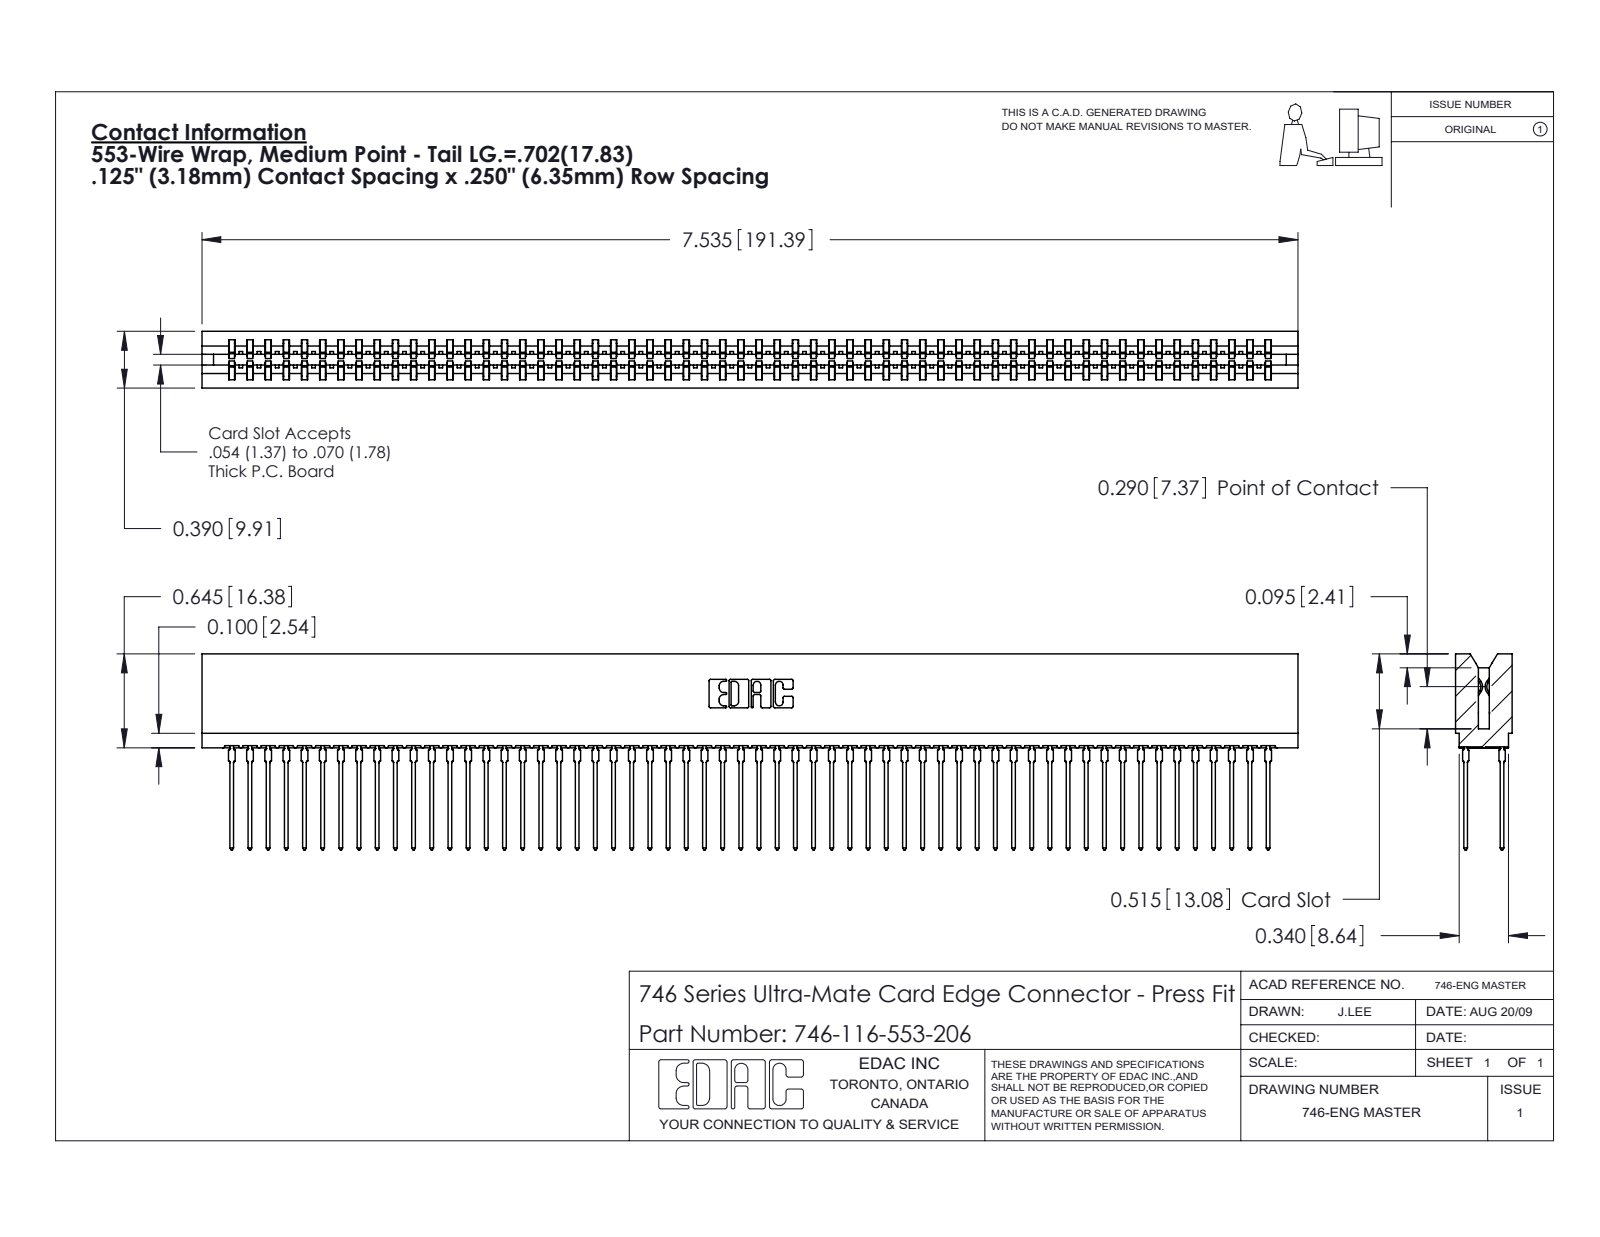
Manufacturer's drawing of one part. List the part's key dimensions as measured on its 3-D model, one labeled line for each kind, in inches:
Part name (STEP PRODUCT): 746 Part_.515 Slot Depth - 06; 746-116-553-206; 746-292-001_553
STEP written by: SolidWorks 2020 (CONFIG_CONTROL_DESIGN)
Units: inches
Bodies: 117 solids, 10480 faces (5392 planar, 2072 cylindrical, 3016 other)
Overall size (bounding box): 7.535 × 1.346 × 0.39
Volume: 1.276 in³ · Surface area: 56.22 in²
Partial cylindrical surfaces — rounded edges, fillets, slot ends (radius × count): R0.021 ×232, R0.015 ×59, R0.01 ×22, R0.005 ×8, R0.011 ×8, R0.007 ×6, R0.031 ×6, R0.026 ×3
Main face-to-face distances: 0.057, 0.333, 0.25, 0.025, 0.307, 0.39, 0.083, 0.275, 0.174, 0.158
